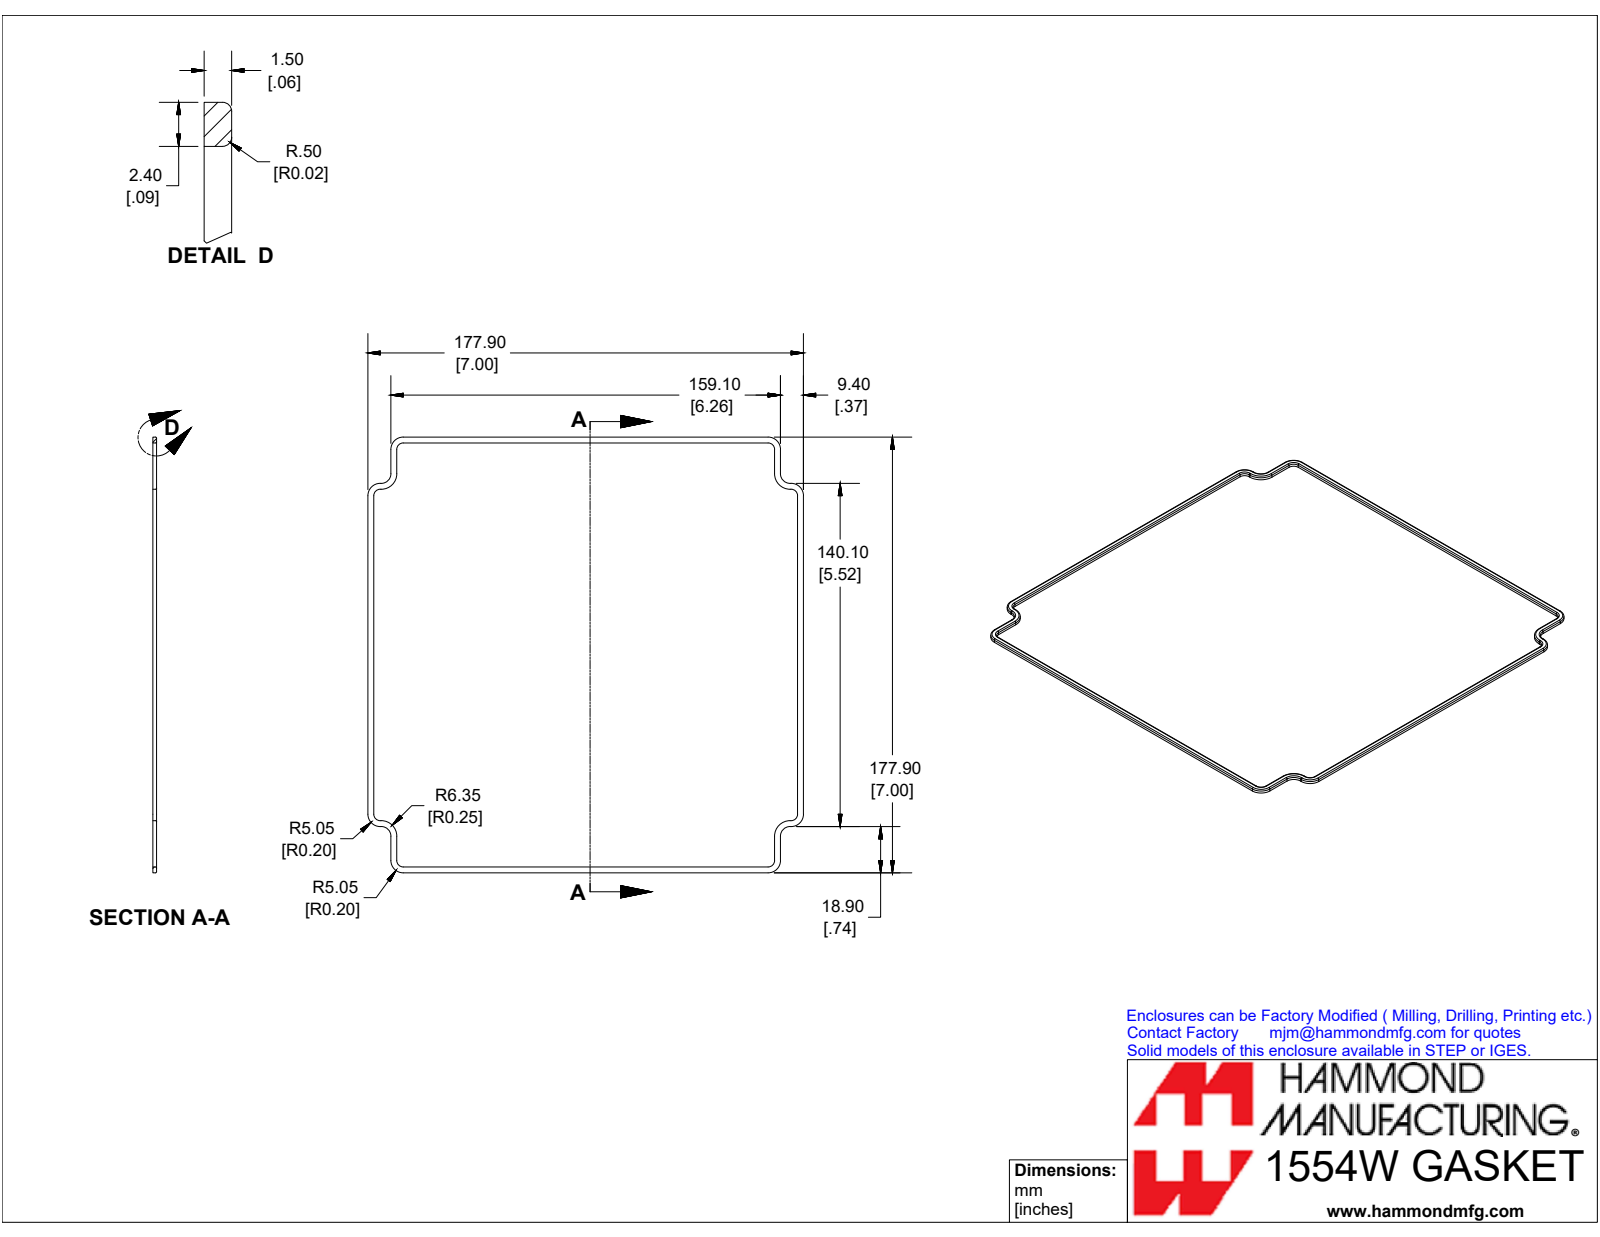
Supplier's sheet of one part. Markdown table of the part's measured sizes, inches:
| quantity | value |
| --- | --- |
| part name | 1554WGASKET |
| STEP written by | SolidWorks 2019 (CONFIG_CONTROL_DESIGN) |
| units | inches |
| bodies | 1 solid, 98 faces (26 planar, 48 cylindrical, 24 other) |
| overall size | 7.004 × 7.004 × 0.059 |
| volume | 0.145 in³ |
| surface area | 7.768 in² |
| partial cylindrical surfaces (radius × count) | 0.02 × 16, 0.104 × 8, 0.199 × 8, 0.156 × 4, 0.25 × 4 |
| main face-to-face distances | 0.059, 0.094, 6.909, 7.004, 6.815, 0.37, 6.539, 0.465, 6.634, 0.276 |
